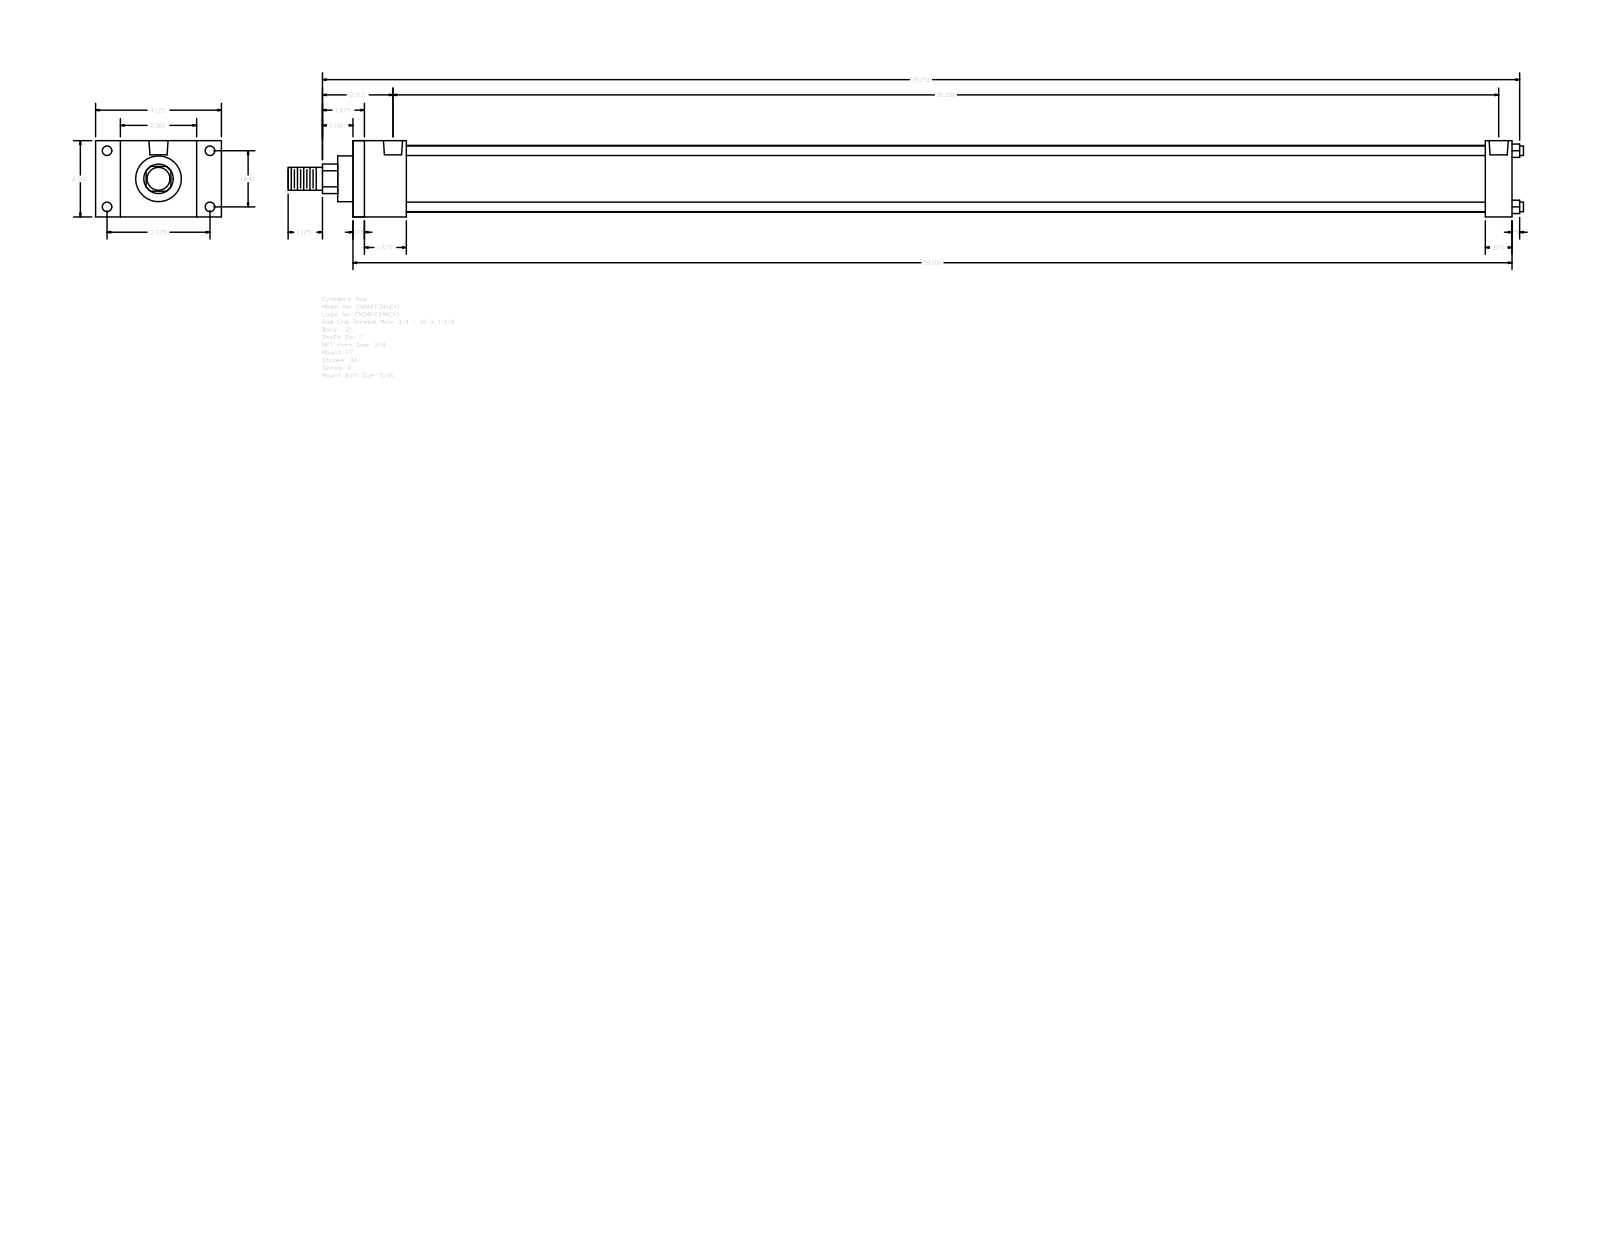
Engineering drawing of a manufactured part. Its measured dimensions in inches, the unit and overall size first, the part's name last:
Units: inches
Overall size (bounding box): 40.5 × 4.125 × 2.5
Round holes (diameter × count): ⌀0.219 ×4, ⌀0.313 ×4, ⌀0.627 ×2
Round bosses / shafts (diameter × count): ⌀0.313 ×4, ⌀2.19 ×1, ⌀1.5 ×1, ⌀1 ×1, ⌀0.75 ×1
Partial cylindrical surfaces — rounded edges, fillets, slot ends (radius × count): R0.484 ×1
Main face-to-face distances: 2.5, 38, 37.625, 0.375, 0.875, 0.813, 1.75, 37.125, 1.375, 36.75
Hole centre spacings: 1.84, 3.375, 3.844, 36.031, 0.063, 0.157, 36.093, 36.187
Bodies: 0 solids, 92 faces (64 planar, 28 cylindrical, 0 other)
Part name (STEP PRODUCT): A_FF__0200_1
STEP written by: GSSL Pune (CONFIG_CONTROL_DESIGN)
